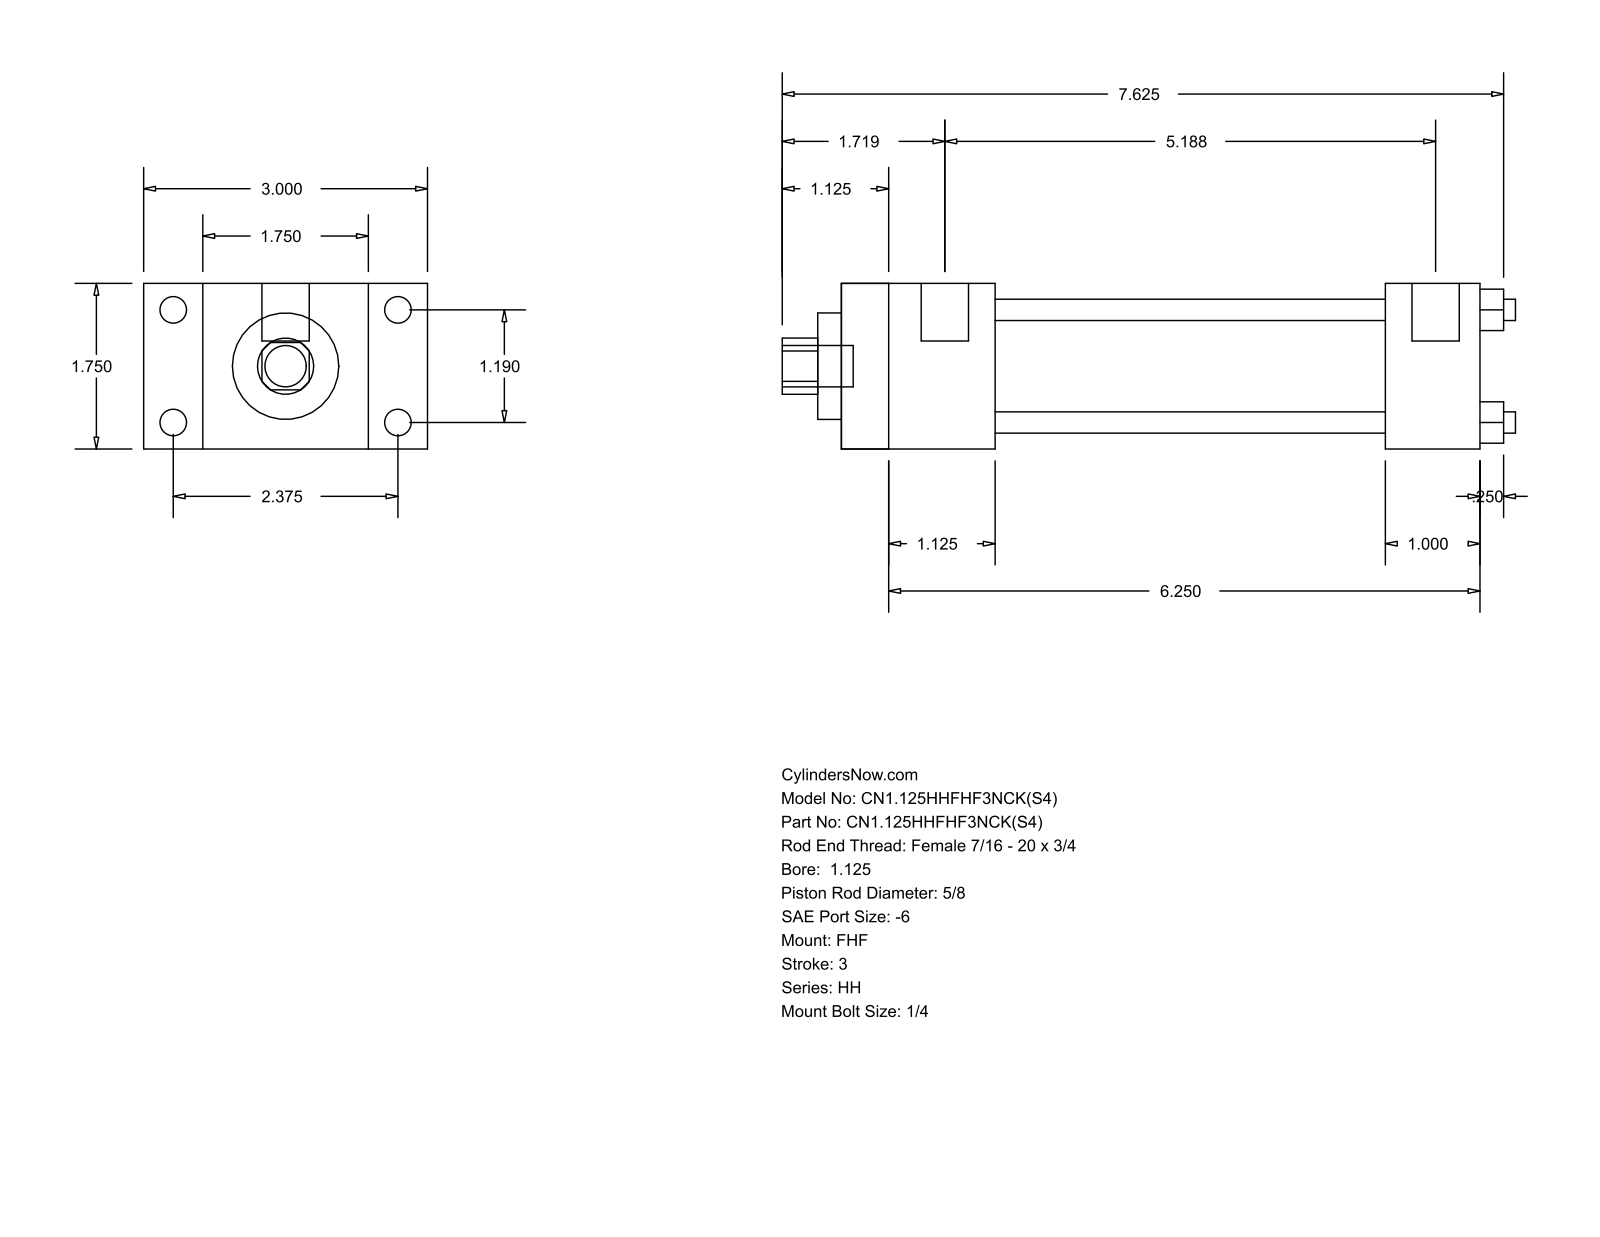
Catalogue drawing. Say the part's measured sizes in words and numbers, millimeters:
The part is named "HH_FHF__0112_0.625". Its 3-D file was written by "GSSL Pune (CONFIG_CONTROL_DESIGN)". It is 0 solids with 88 faces: 60 planar, 28 cylindrical and 0 other. Overall it measures 196.85 by 76.2 by 44.45 millimeters. Round holes: 4 of diameter 5.71, 1 of diameter 15.88, 1 of diameter 28.57, 1 of diameter 34.92. Round bosses or shafts: 4 of diameter 7.14, 4 of diameter 5.56, 2 of diameter 12.7, 1 of diameter 11.11. Partial cylindrical surfaces (rounded edges, fillets, slot ends): 1 of radius 7.54. The main face-to-face distances are 44.46, 15.87, 60.33, 41.27, 76.2, 171.44, 130.17, 146.05, 104.78, 25.39. The hole center spacings are 21.37, 30.22, 42.74.
